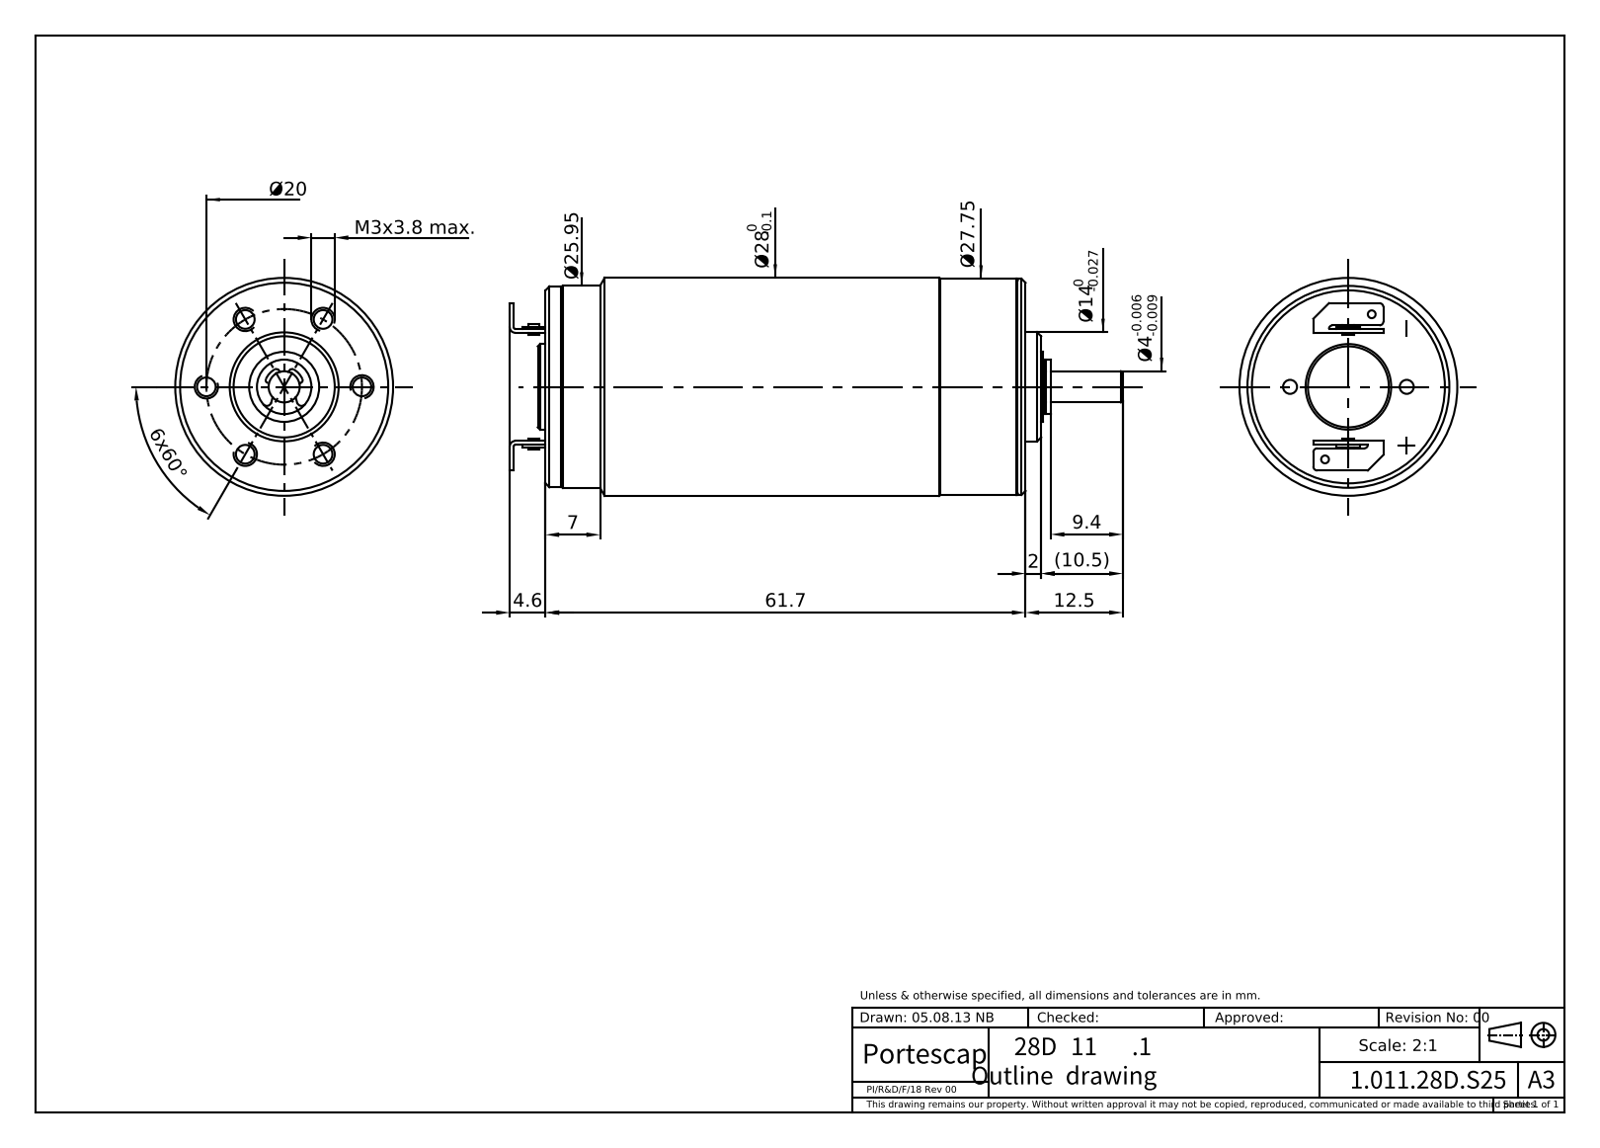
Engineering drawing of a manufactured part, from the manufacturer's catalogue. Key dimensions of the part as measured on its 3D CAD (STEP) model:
Part name (STEP PRODUCT): PRT0007
STEP written by: PRO/ENGINEER BY PARAMETRIC TECHNOLOGY CORPORATION, 2014310 (CONFIG_CONTROL_DESIGN)
Units: millimetres
Bodies: 1 solid, 141 faces (48 planar, 65 cylindrical, 28 other)
Overall size (bounding box): 77.1 × 28 × 28
Volume: 38 587 mm³ · Surface area: 7 424 mm²
Round holes (diameter × count): ⌀2.5 ×6, ⌀3 ×6, ⌀1.5 ×4
Round bosses / shafts (diameter × count): ⌀28 ×1, ⌀27.75 ×1, ⌀25.95 ×1, ⌀25.8 ×1, ⌀14 ×1, ⌀9 ×1, ⌀7 ×1, ⌀4 ×1
Partial cylindrical surfaces — rounded edges, fillets, slot ends (radius × count): R0.3 ×4, R1.5 ×4, R0.5 ×2, R2.08 ×1, R3 ×1, R10.6 ×1
Main face-to-face distances: 64.6, 2, 62.6, 0.6, 62, 2.6, 64, 66.6, 0.4, 1
Hole centre spacings: 10, 17.32, 19.64, 20, 2.79, 2.82, 4.65, 5.8
